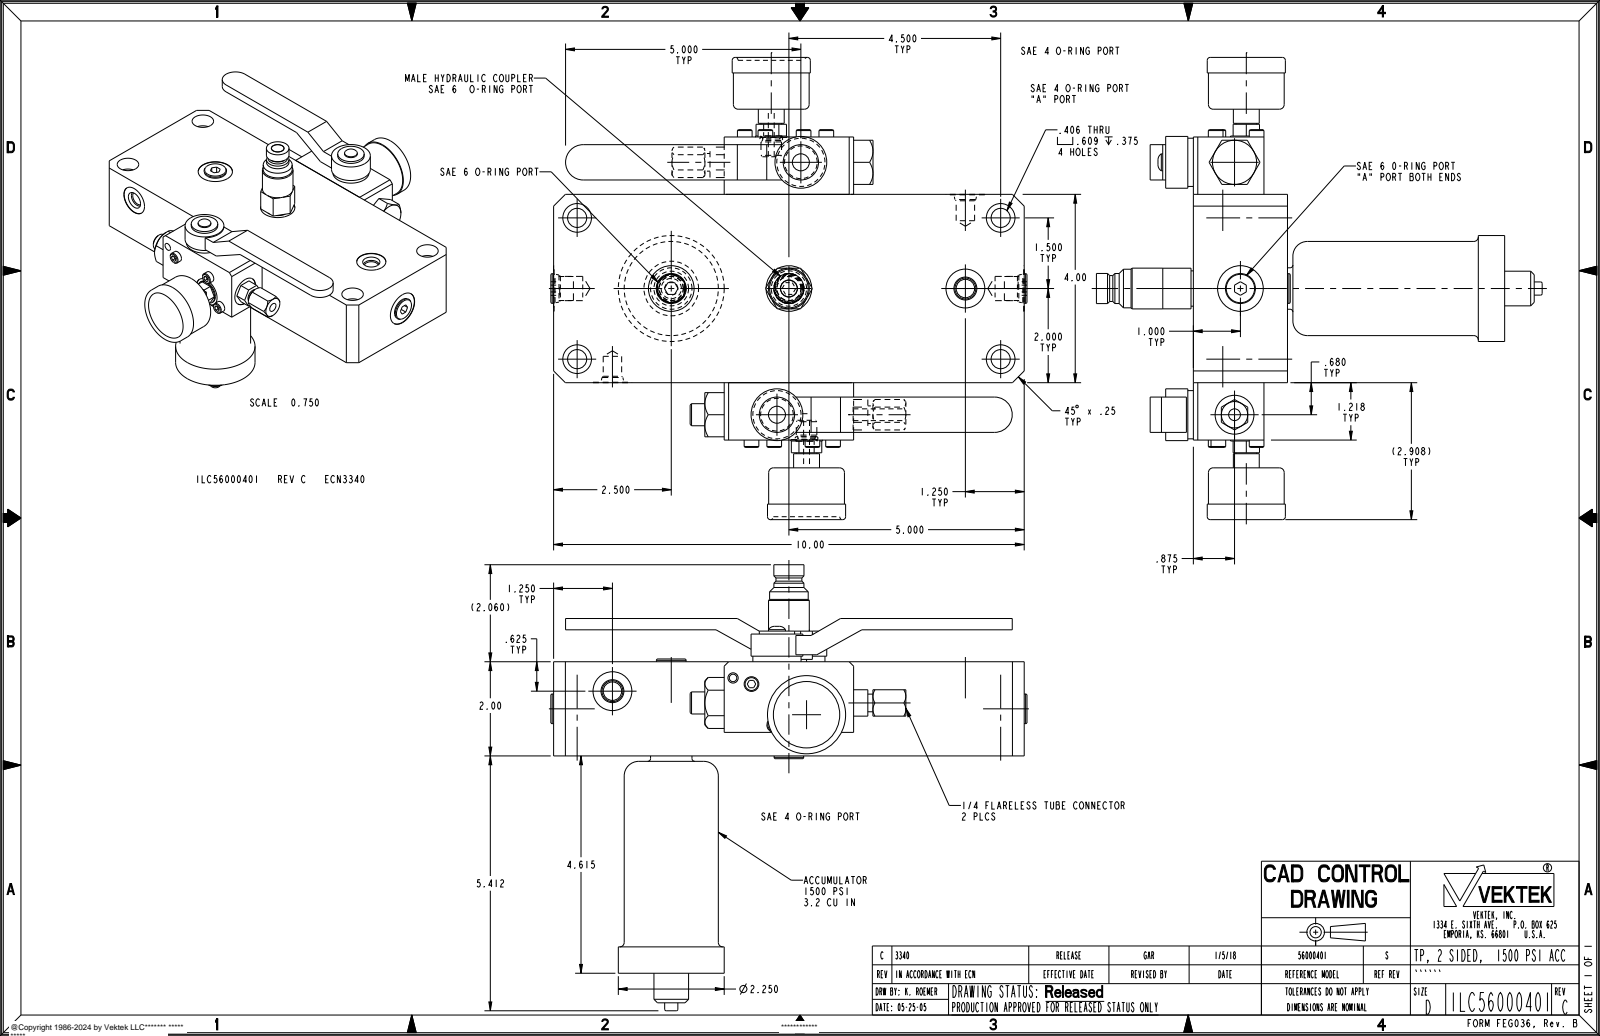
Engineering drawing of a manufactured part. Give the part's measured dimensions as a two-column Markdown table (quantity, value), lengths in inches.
| quantity | value |
| --- | --- |
| part name | ILC56000401_PLATE; ILC56000401_70101703; ILC56000401_70101700; ILC56000401_72212155 (+1 more) |
| STEP written by | PRO/ENGINEER BY PARAMETRIC TECHNOLOGY CORPORATION, 2013320 (AUTOMOTIVE_DESIGN) |
| units | inches |
| bodies | 9 solids, 859 faces (373 planar, 274 cylindrical, 212 other) |
| overall size | 10.118 × 9.816 × 9.472 |
| volume | 110.9 in³ |
| surface area | 330.2 in² |
| round holes (diameter × count) | 0.218 × 12, 0.159 × 8, 0.392 × 7, 0.825 × 7, 0.188 × 4, 0.406 × 4, 0.5 × 4, 0.609 × 4, 0.515 × 3, 0.97 × 3, 0.125 × 2, 0.25 × 2 |
| round bosses / shafts (diameter × count) | 0.312 × 8, 0.437 × 5, 0.75 × 3, 0.563 × 3, 0.51 × 3, 1.66 × 2, 1.61 × 2, 1.1 × 2 |
| partial cylindrical surfaces (radius × count) | 0.375 × 2 |
| main face-to-face distances | 2, 4, 0.5, 1.218, 5.218, 1.5, 10, 2.918, 2.418, 0.918 |
| hole center spacings | 4.743, 2.5, 0.228, 0.3, 0.413, 0.604, 0.607, 0.626 |
